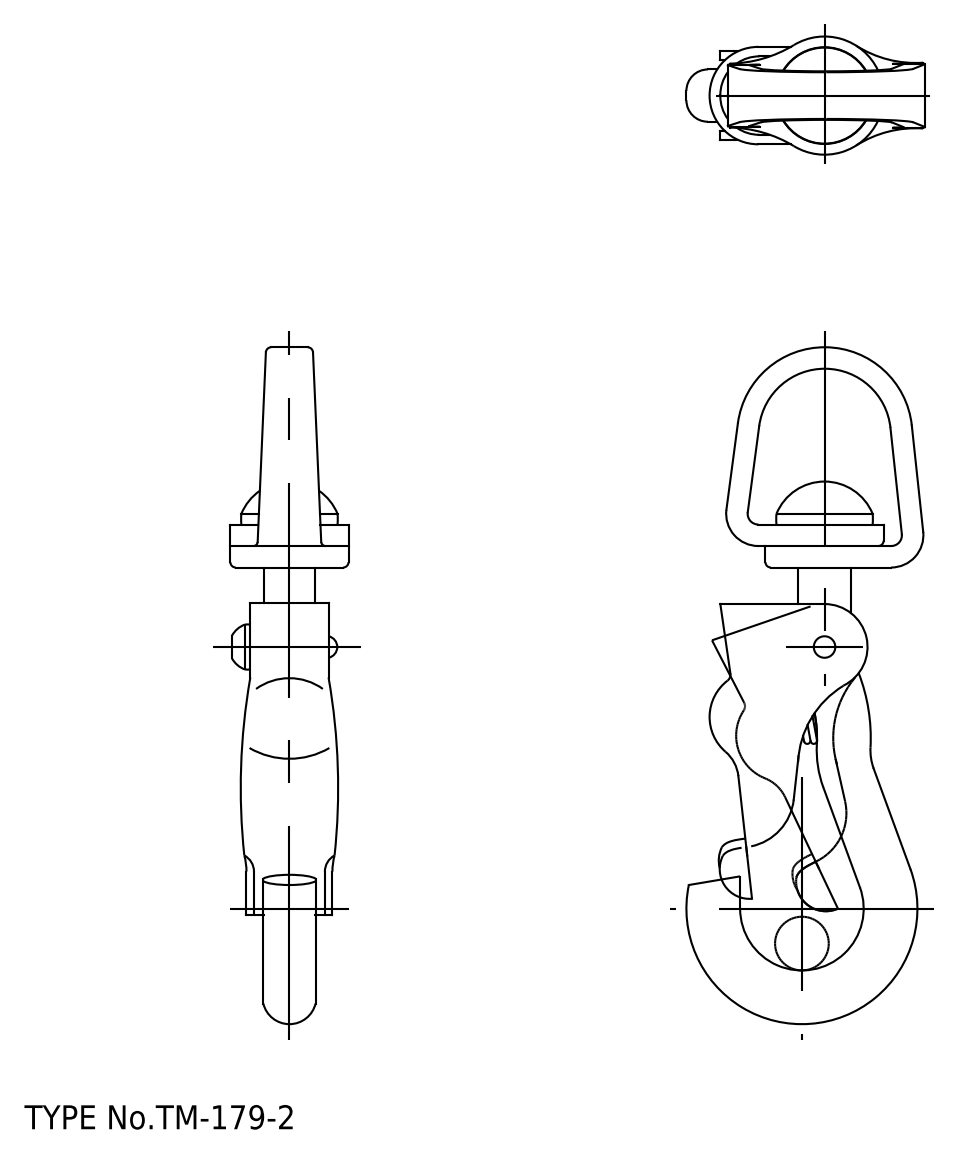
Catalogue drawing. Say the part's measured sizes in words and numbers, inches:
The part is named "Dカン; フック; レバー". Its 3-D file was written by "spGate 20.6.3 (****-****-****-****) (AUTOMOTIVE_DESIGN)". It is 3 solids with 162 faces: 39 planar, 68 cylindrical and 55 other. Overall it measures 3.11 by 1.096 by 0.543 inches. Its volume is 0.33 cubic inches and its surface area 8.547 square inches. Round holes: 1 of diameter 0.099, 1 of diameter 0.335. Round bosses or shafts: 1 of diameter 0.543. Partial cylindrical surfaces (rounded edges, fillets, slot ends): 10 of radius 0.098, 3 of radius 0.035, 3 of radius 0.074, 2 of radius 0.039, 2 of radius 0.049, 2 of radius 0.138, 2 of radius 0.148, 2 of radius 0.177. The main face-to-face distances are 0.021, 0.261, 0.099, 0.039, 0.06, 0.3, 0.321, 0.24, 0.198, 0.282.
